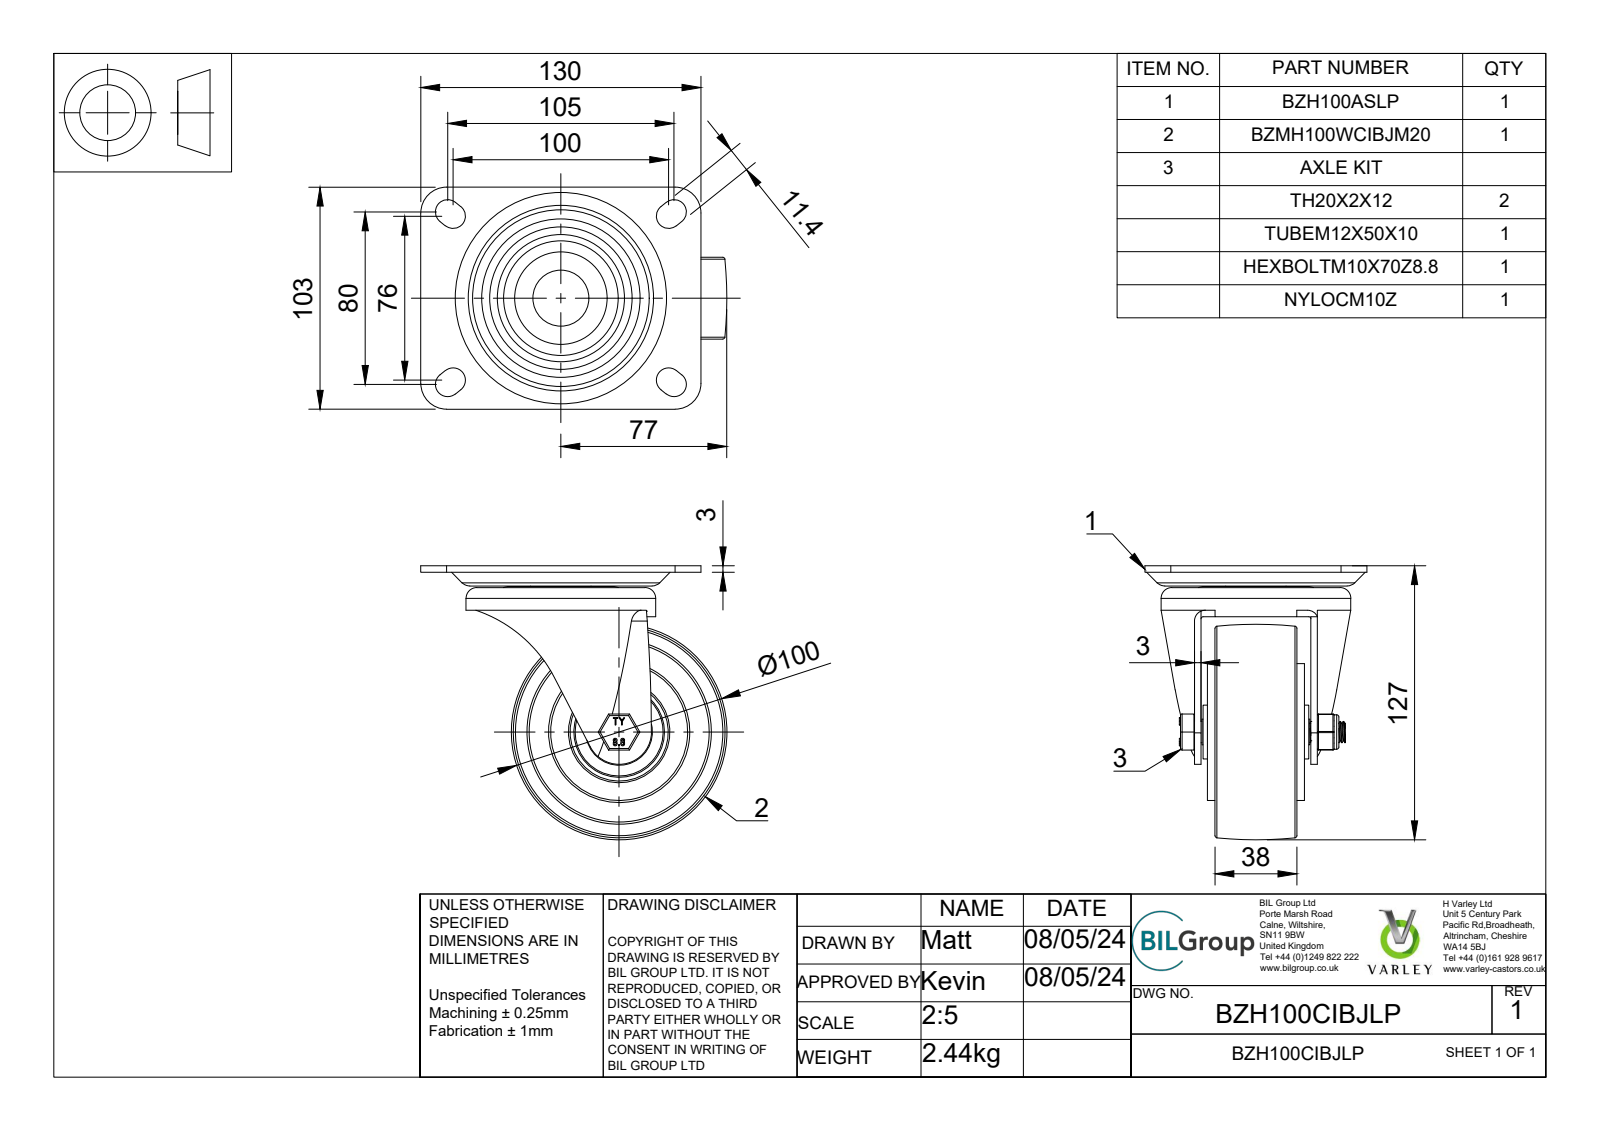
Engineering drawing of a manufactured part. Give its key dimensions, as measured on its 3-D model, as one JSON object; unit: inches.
{"part_name": "BZH100CIBJLP v3; BZH100ASLP v1; ZINC PLATED PRESSED STEEL FORK; ZINC PLATED PRESSED STEEL TOP PLATE (+7 more)", "step_written_by": "Autodesk Translation Framework v12.20.1.177 (AUTOMOTIVE_DESIGN)", "units": "inches", "bodies": {"solids": 36, "faces": 1034, "planar": 407, "cylindrical": 195, "other": 432}, "overall_size": [5.591, 5.005, 4.055], "volume_in3": 18.98, "surface_area_in2": 240.4, "round_holes": [[0.394, 1], [0.402, 1], [0.413, 1], [0.472, 1], [0.48, 1], [0.787, 1], [1.122, 1], [1.181, 1], [1.213, 1], [1.587, 1], [1.594, 1], [1.654, 1]], "round_bosses_or_shafts": [[3.465, 1], [2.5, 1], [1.606, 1], [1.417, 1], [1.232, 1], [1.102, 1], [1.063, 1], [1.024, 1]], "partial_cylinders_radius": [[0.02, 18], [0.224, 8], [0.03, 6], [0.472, 4], [0.039, 2], [0.197, 2], [0.591, 1], [0.65, 1]], "face_to_face_distances": [0.118, 0.138, 0.551, 1.083, 0.689, 0.531, 1.22, 0.669, 0.02, 0.394]}
